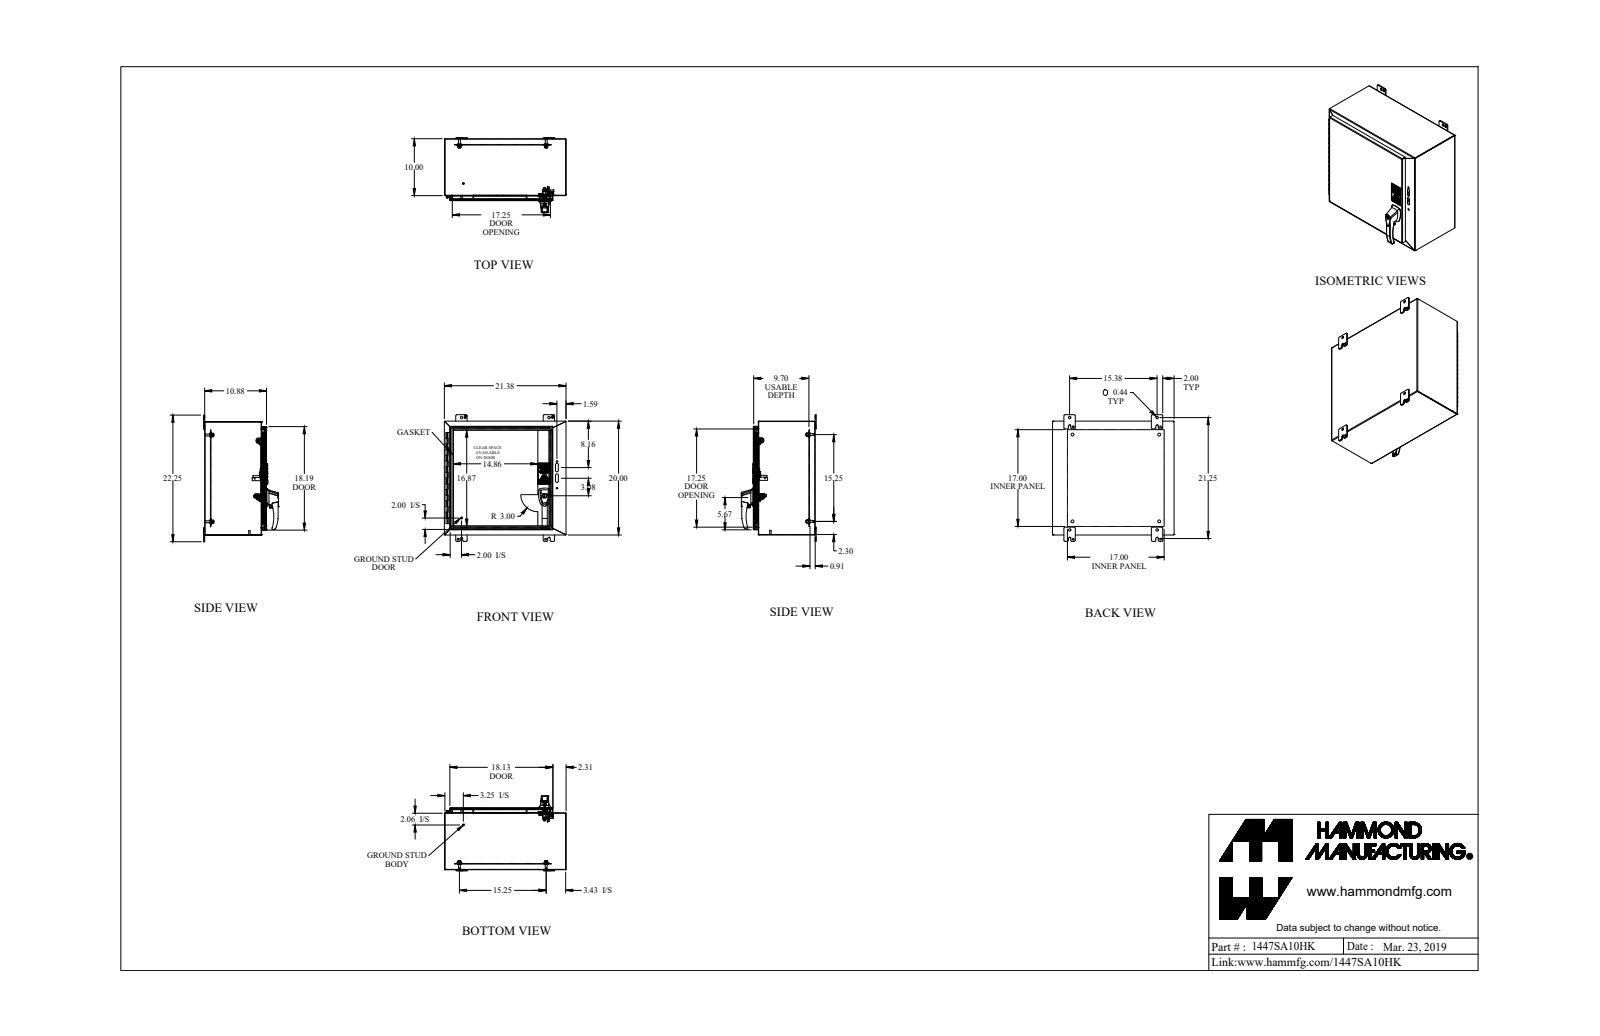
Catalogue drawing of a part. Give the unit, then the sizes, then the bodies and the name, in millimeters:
Units: millimetres
Overall size (bounding box): 565.2 × 542.9 × 334.7
Round holes (diameter × count): ⌀8 ×5, ⌀4.5 ×4, ⌀11.1 ×4, ⌀12.7 ×4, ⌀4 ×2, ⌀4.4 ×2, ⌀5.5 ×2, ⌀6.4 ×2, ⌀6.7 ×2, ⌀7.1 ×2, ⌀7.8 ×2, ⌀10.5 ×2
Round bosses / shafts (diameter × count): ⌀9.5 ×8, ⌀6.4 ×7, ⌀25.4 ×4, ⌀16.5 ×4, ⌀8.4 ×4, ⌀4 ×4, ⌀12.7 ×2, ⌀10.2 ×2
Partial cylindrical surfaces — rounded edges, fillets, slot ends (radius × count): R4.8 ×24, R6.4 ×24, R0.9 ×20, R2.7 ×20, R3.2 ×9, R5.5 ×8, R1.5 ×7, R0.8 ×6
Main face-to-face distances: 1.8, 274.4, 506.2, 541.1, 272.6, 276.2, 2.4, 248.2, 246.4, 26.2
Hole centre spacings: 387.4, 390.5, 547.8, 28.2, 44.1, 44.1, 47.1, 89.3
Volume: 3 025 000 mm³ · Surface area: 2 973 000 mm²
Bodies: 49 solids, 1178 faces (734 planar, 321 cylindrical, 123 other)
Part name (STEP PRODUCT): 1447SA10HK
STEP written by: SolidWorks 2019 (AUTOMOTIVE_DESIGN)
